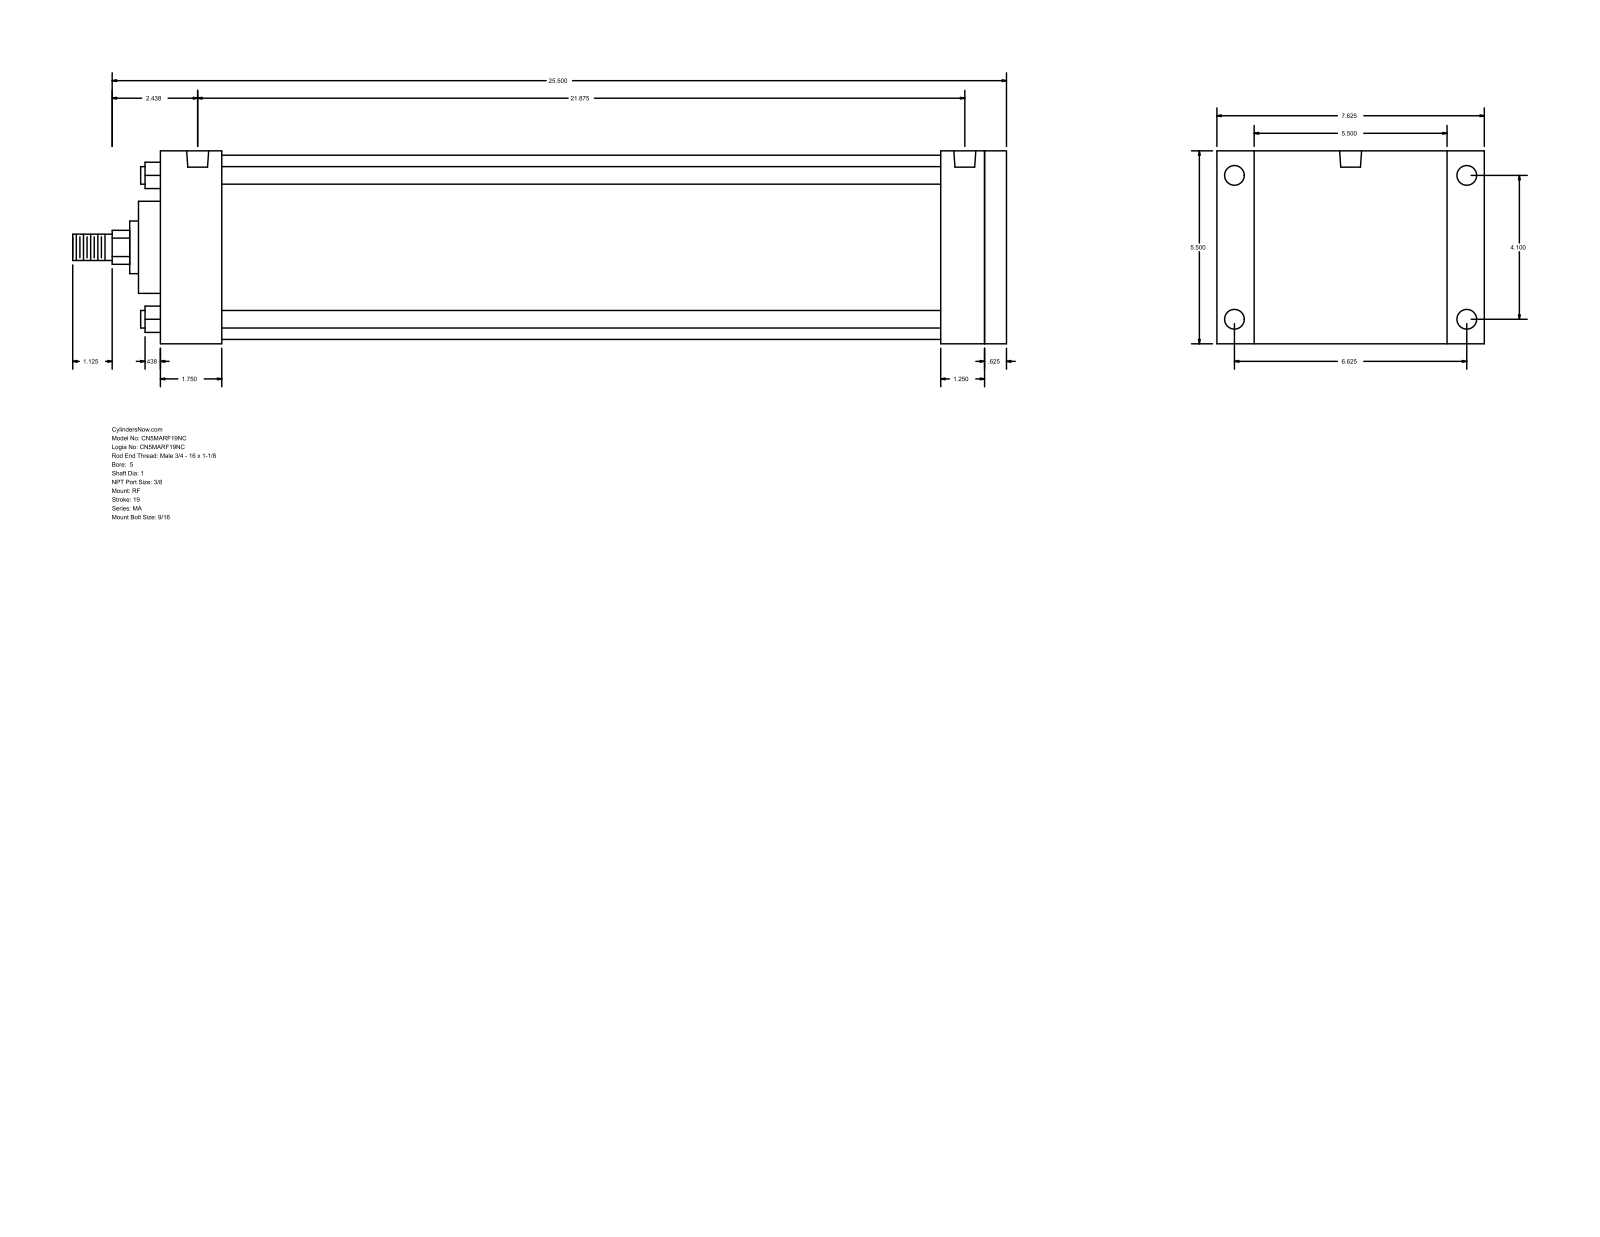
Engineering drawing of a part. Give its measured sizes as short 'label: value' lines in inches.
name: MA_RF__0500_1
written by: GSSL Pune (CONFIG_CONTROL_DESIGN)
unit: in
bodies: 0 solids, 94 faces (65 planar, 29 cylindrical, 0 other)
size: 26.625 × 7.625 × 5.5
holes: 4× ⌀0.437, 4× ⌀0.563, 2× ⌀0.627
bosses: 4× ⌀0.5, 1× ⌀5.25, 1× ⌀2.625, 1× ⌀1.5, 1× ⌀1, 1× ⌀0.75
rounds: 1× R0.484
face distances: 5.5, 24.125, 0.625, 23.5, 1.875, 1.75, 21.75, 22.375, 22.25, 20.5
hole spacings: 4.1, 6.625, 7.791, 21.5, 0.187, 0.188, 21.687, 21.688
